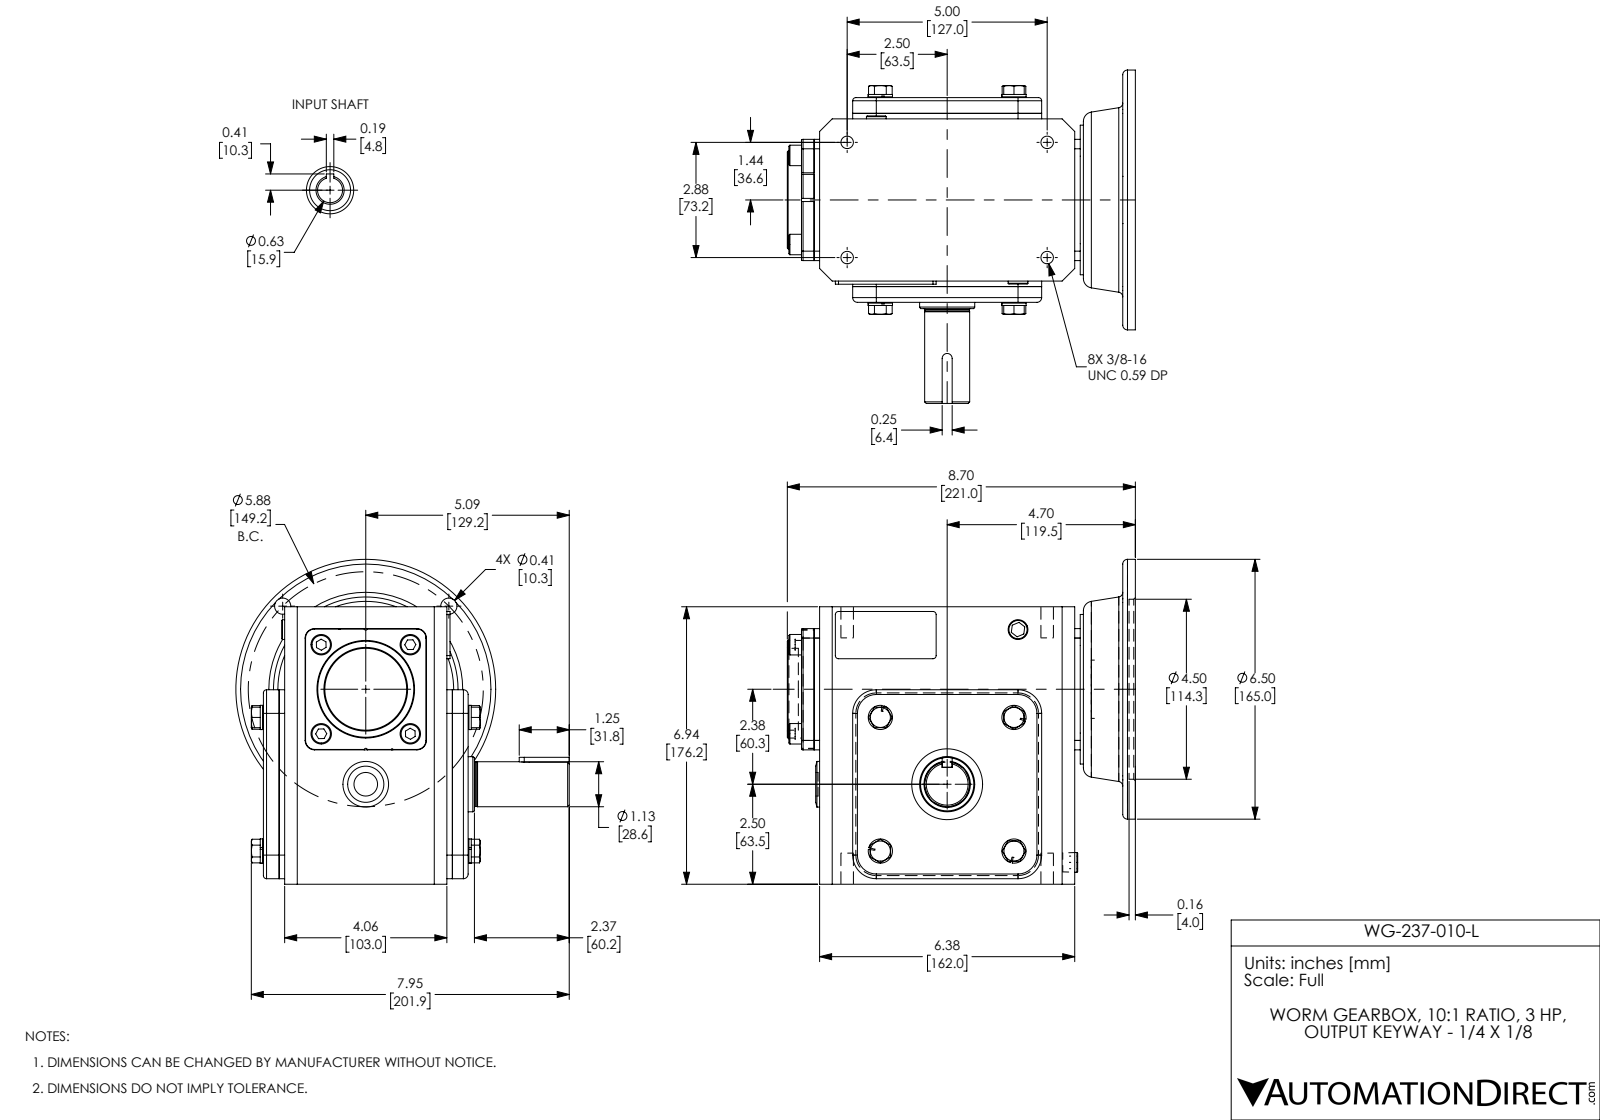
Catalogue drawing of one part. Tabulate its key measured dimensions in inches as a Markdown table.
| quantity | value |
| --- | --- |
| part name | WG-237-010-L |
| STEP written by | SolidWorks 2017 (AUTOMOTIVE_DESIGN) |
| units | inches |
| bodies | 37 solids, 542 faces (295 planar, 157 cylindrical, 90 other) |
| overall size | 8.701 × 8.335 × 8.123 |
| volume | 220.2 in³ |
| surface area | 513.5 in² |
| round holes (diameter × count) | 0.313 × 4, 0.406 × 4, 0.591 × 1, 0.625 × 1, 1.181 × 1, 1.378 × 1, 1.457 × 1, 1.772 × 1, 3.819 × 1, 4.5 × 1 |
| round bosses / shafts (diameter × count) | 0.606 × 4, 0.512 × 4, 6.496 × 1, 3.74 × 1, 2.441 × 1, 2.047 × 1, 1.142 × 1, 1.125 × 1 |
| partial cylindrical surfaces (radius × count) | 0.079 × 12, 0.236 × 6, 0.118 × 4, 0.591 × 4, 0.02 × 2, 0.039 × 2, 0.125 × 1 |
| main face-to-face distances | 0.138, 4.724, 0.394, 4.331, 0.531, 4.193, 4.587, 6.516, 6.937, 0.315 |
| hole center spacings | 2.937, 2.098, 2.88, 4.154, 4.154, 4.913, 5, 5.77 |
